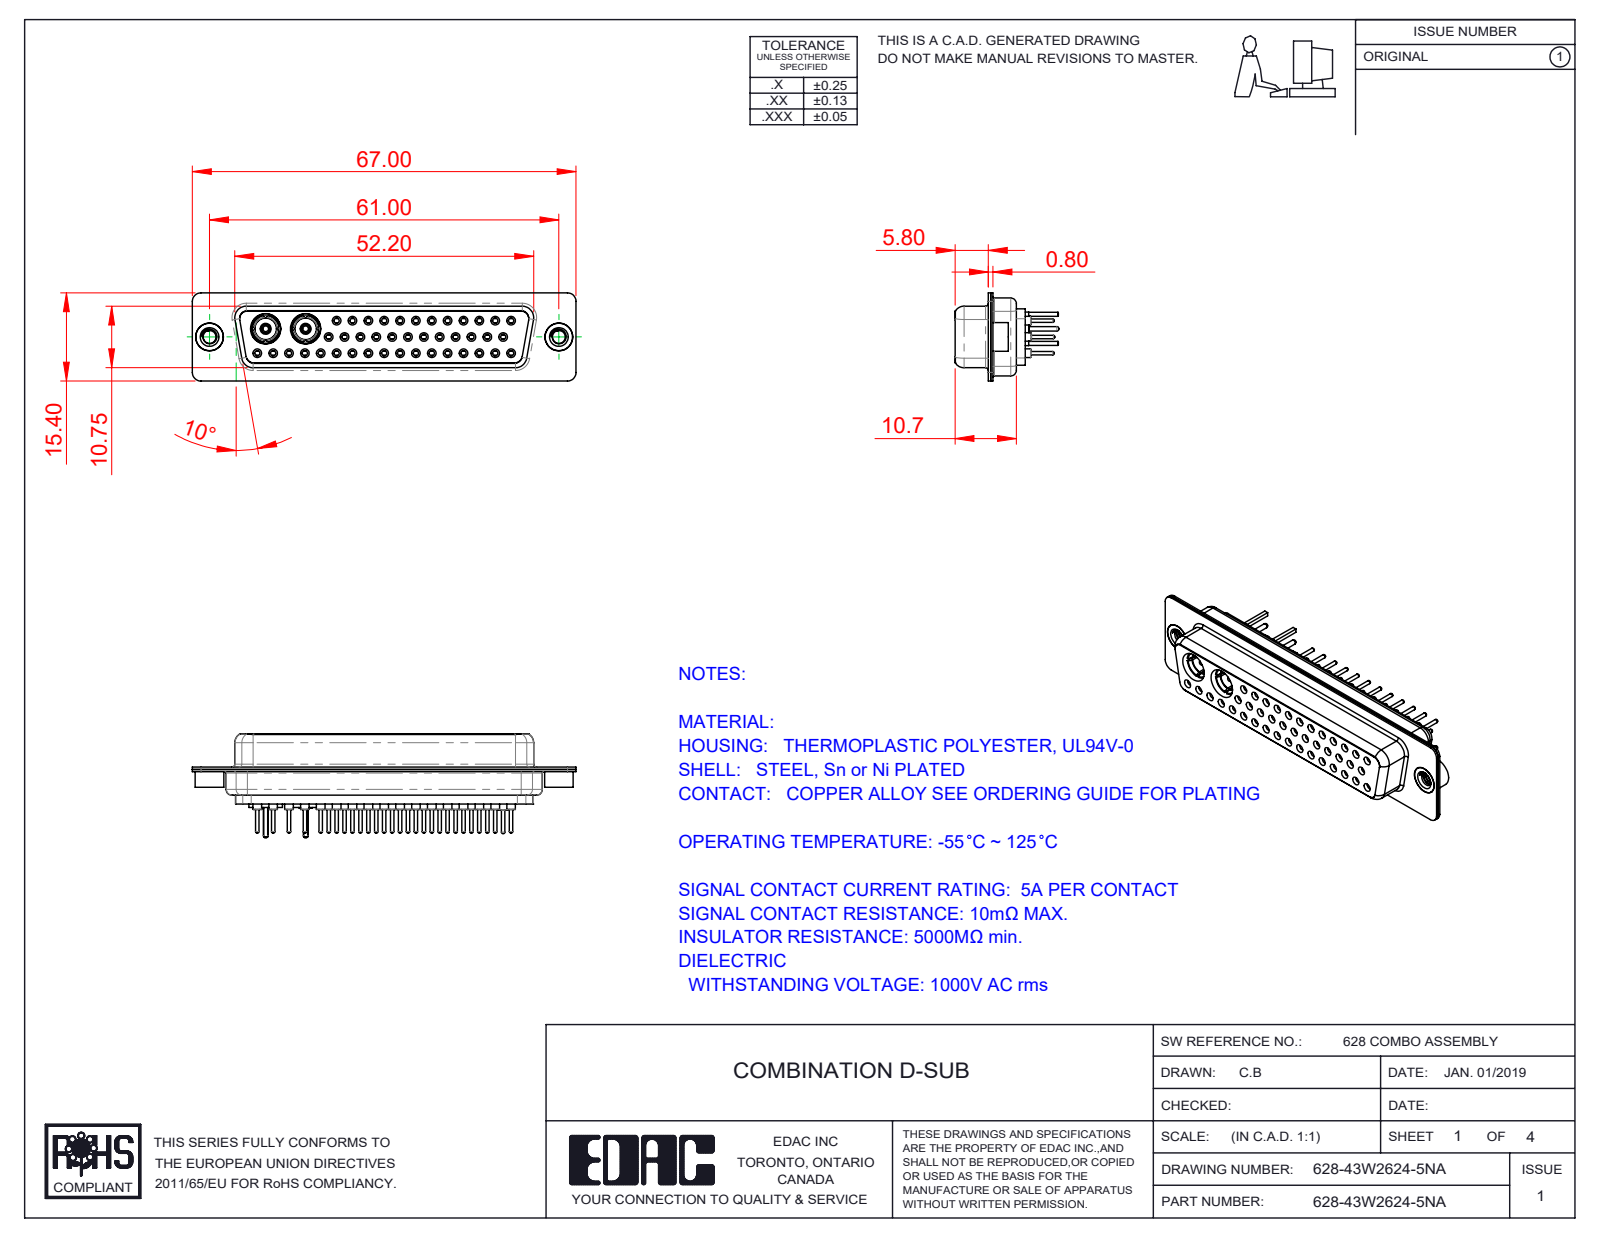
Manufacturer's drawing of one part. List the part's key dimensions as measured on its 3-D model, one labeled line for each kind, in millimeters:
Part name (STEP PRODUCT): 628Combo Shell Front_50 Contacts; 628Combo Housing_43W2; 628Combo Threaded Rivet_A; Pin_Str (+8 more)
STEP written by: SolidWorks 2016 (CONFIG_CONTROL_DESIGN)
Units: millimetres
Bodies: 54 solids, 2786 faces (796 planar, 1008 cylindrical, 982 other)
Overall size (bounding box): 67 × 18.15 × 15.4
Volume: 6 932 mm³ · Surface area: 14 979 mm²
Round holes (diameter × count): ⌀1.1 ×43, ⌀1.5 ×43, ⌀0.9 ×41, ⌀2 ×41, ⌀1.6 ×29, ⌀1.7 ×12, ⌀4.85 ×4, ⌀2.26 ×2, ⌀2.83 ×2, ⌀3.3 ×2, ⌀3.92 ×2, ⌀4 ×2
Round bosses / shafts (diameter × count): ⌀2.2 ×41, ⌀0.6 ×41, ⌀1.6 ×12, ⌀5 ×4, ⌀5.85 ×2, ⌀5.2 ×2, ⌀4.95 ×2, ⌀4.8 ×2
Partial cylindrical surfaces — rounded edges, fillets, slot ends (radius × count): R1.5 ×16, R1.35 ×12, R2 ×12, R1.6 ×8, R0.25 ×4, R0.5 ×4, R0.6 ×4, R0.65 ×4
Main face-to-face distances: 0.4, 6.05, 6.45, 11.33, 1.87, 10.35, 10.93, 12.25, 6.2, 5.8
Hole centre spacings: 2.77, 3.16, 5.54, 8.31, 11.08, 13.85, 16.62, 19.39
